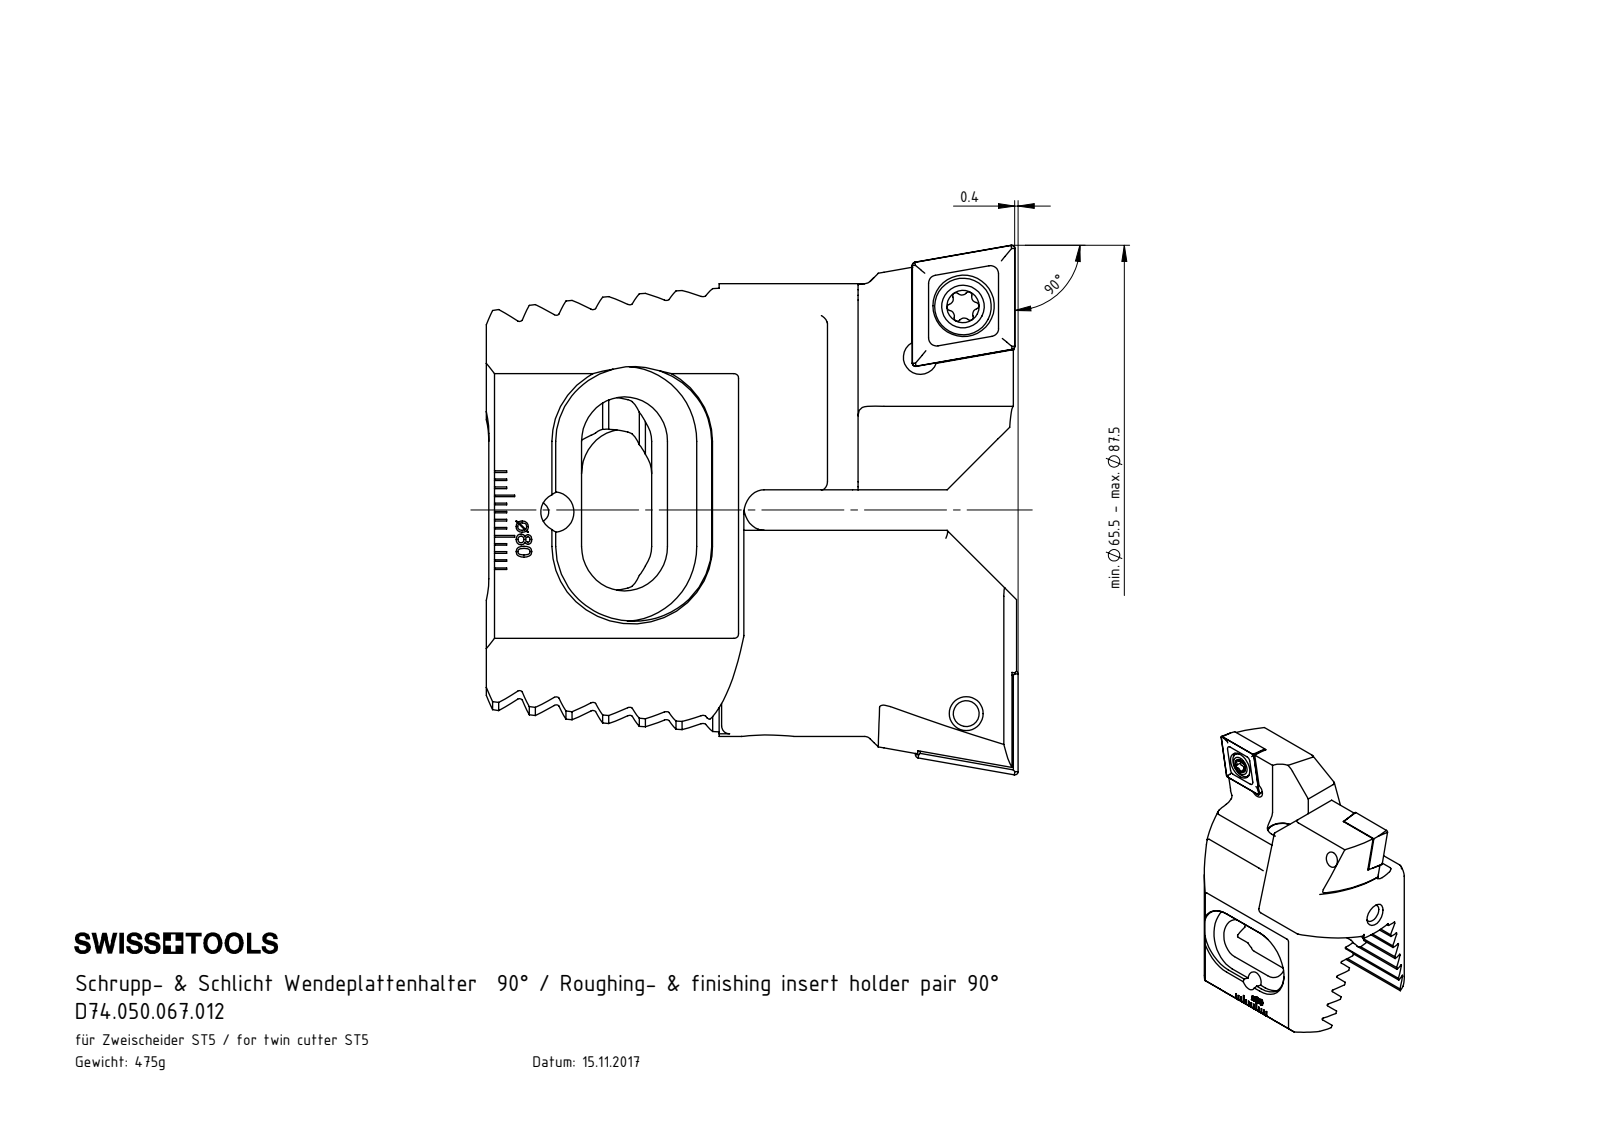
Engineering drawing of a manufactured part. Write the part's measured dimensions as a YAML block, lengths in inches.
part_name: "CCMT120404; ZC5-xxx.001.037_A; ISO 4028 - M3 x 5_M3x8; D74.050.067.012 (+3 more)"
step_written_by: "SolidWorks 2017 (CONFIG_CONTROL_DESIGN)"
units: inches
bodies: {solids: 8, faces: 706, planar: 349, cylindrical: 137, other: 220}
overall_size: [2.591, 2.579, 1.74]
volume: 3.717
surface_area: 34.75
round_holes:
  - {diameter: 0.165, count: 4}
  - {diameter: 0.197, count: 2}
  - {diameter: 0.217, count: 2}
  - {diameter: 0.299, count: 2}
  - {diameter: 0.079, count: 1}
  - {diameter: 0.098, count: 1}
  - {diameter: 0.315, count: 1}
round_bosses_or_shafts:
  - {diameter: 0.276, count: 2}
  - {diameter: 0.197, count: 2}
  - {diameter: 0.236, count: 1}
  - {diameter: 0.157, count: 1}
  - {diameter: 0.118, count: 1}
  - {diameter: 0.079, count: 1}
partial_cylinders:
  - {radius: 0.039, count: 14}
  - {radius: 0.013, count: 12}
  - {radius: 0.015, count: 12}
  - {radius: 0.027, count: 6}
  - {radius: 0.027, count: 6}
  - {radius: 0.118, count: 4}
  - {radius: 0.217, count: 4}
  - {radius: 0.364, count: 4}
face_to_face_distances: [0.16, 0.32, 0.481, 0.641, 0.801, 0.309, 0.067, 0.683, 1.057, 1.74]
hole_center_spacings: [1.748, 1.752, 1.985, 0.318, 0.323, 0.323, 0.328, 0.63]
